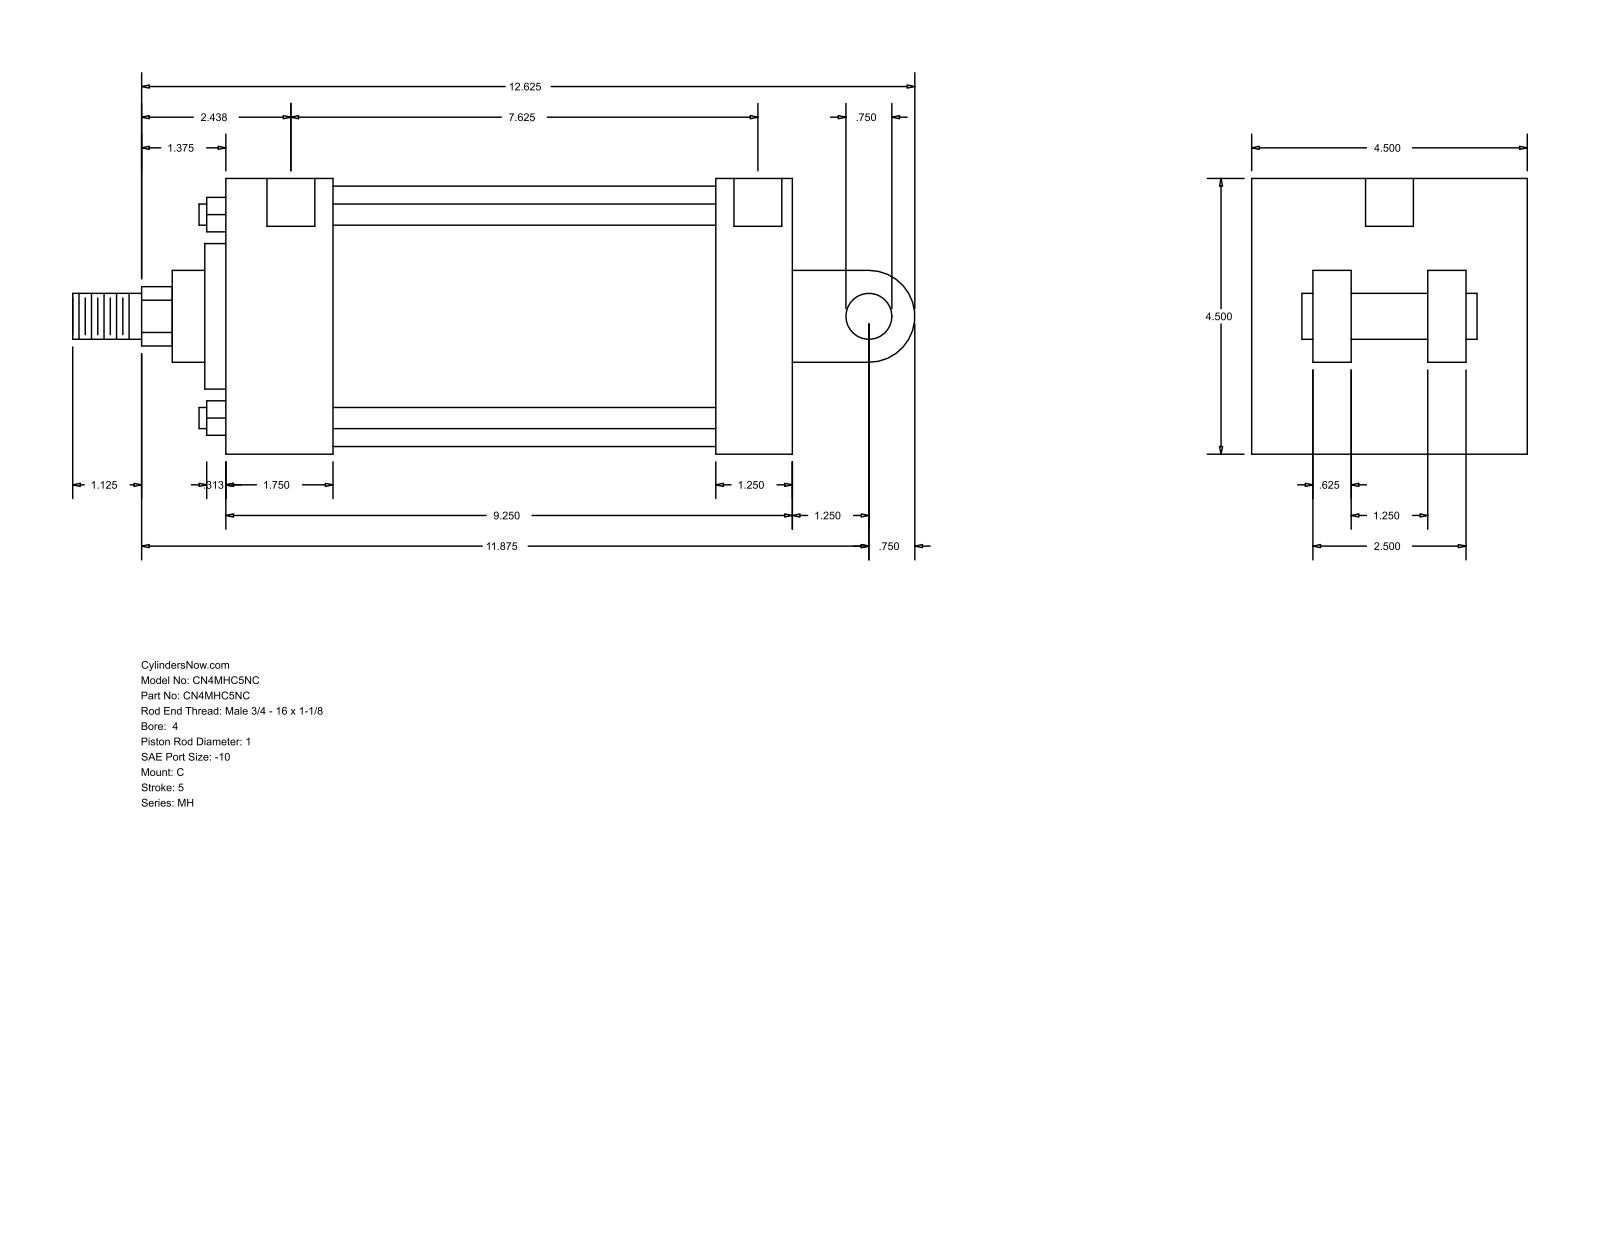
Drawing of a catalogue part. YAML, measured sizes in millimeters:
part_name: "MH_C__0400_1"
step_written_by: "GSSL Pune (CONFIG_CONTROL_DESIGN)"
units: millimeters
bodies: {solids: 0, faces: 101, planar: 71, cylindrical: 30, other: 0}
overall_size: [349.25, 114.3, 114.3]
round_holes:
  - {diameter: 8.73, count: 4}
  - {diameter: 19.84, count: 2}
round_bosses_or_shafts:
  - {diameter: 8.76, count: 4}
  - {diameter: 19.05, count: 2}
  - {diameter: 107.95, count: 1}
  - {diameter: 60.33, count: 1}
  - {diameter: 38.1, count: 1}
  - {diameter: 25.4, count: 1}
partial_cylinders:
  - {radius: 12.29, count: 1}
  - {radius: 19.05, count: 1}
face_to_face_distances: [114.3, 234.96, 31.76, 44.46, 203.2, 158.74, 190.5, 73.03, 41.27, 38.1]
hole_center_spacings: [196.85, 1.58, 1.59, 193.68, 195.26, 195.27]
